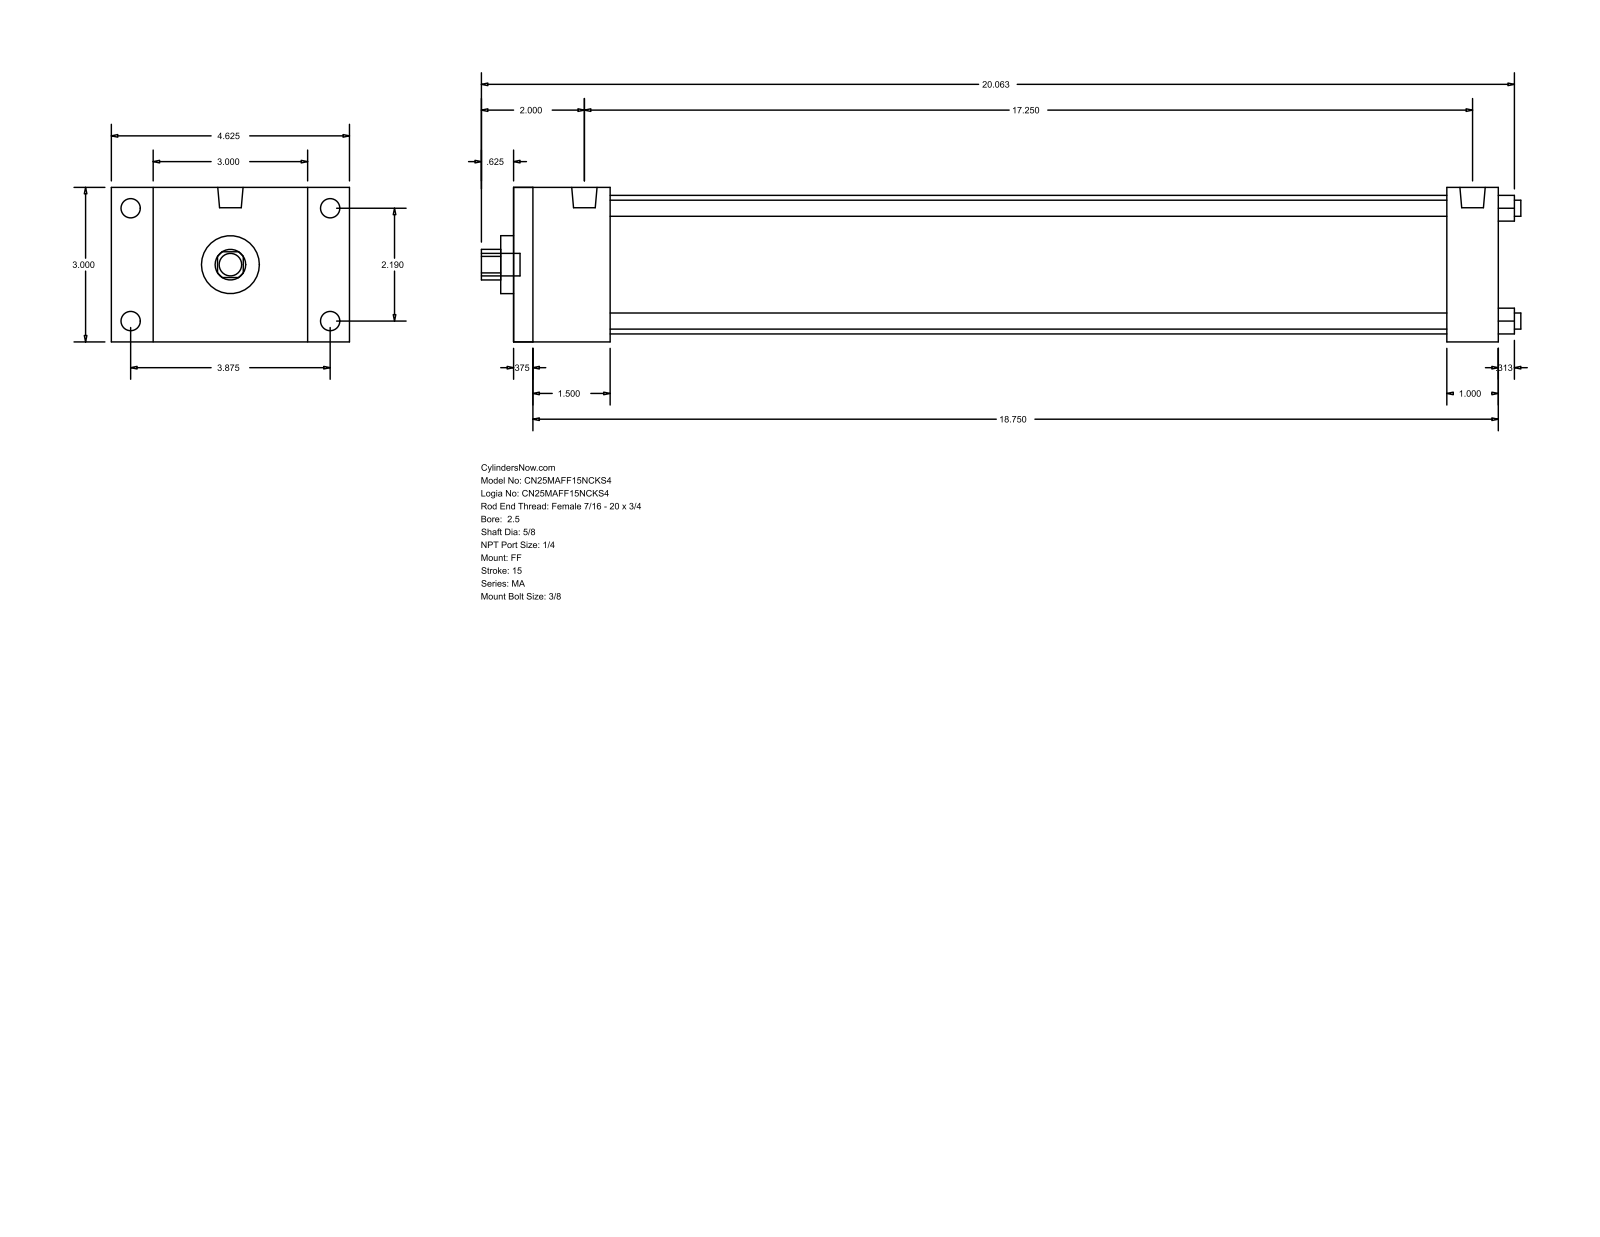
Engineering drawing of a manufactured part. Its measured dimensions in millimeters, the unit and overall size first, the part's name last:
Units: millimetres
Overall size (bounding box): 512.76 × 117.47 × 76.2
Round holes (diameter × count): ⌀7.94 ×4, ⌀15.88 ×1, ⌀28.57 ×1, ⌀68.33 ×1
Round bosses / shafts (diameter × count): ⌀9.53 ×4, ⌀7.94 ×4, ⌀12.49 ×2, ⌀11.11 ×1
Partial cylindrical surfaces — rounded edges, fillets, slot ends (radius × count): R7.54 ×1
Main face-to-face distances: 76.2, 485.77, 9.52, 476.25, 25.4, 47.62, 460.37, 38.1, 450.85, 412.75
Hole centre spacings: 39.33, 55.62, 78.66
Bodies: 0 solids, 92 faces (64 planar, 28 cylindrical, 0 other)
Part name (STEP PRODUCT): MA_FF__0250_0.625
STEP written by: GSSL Pune (CONFIG_CONTROL_DESIGN)
